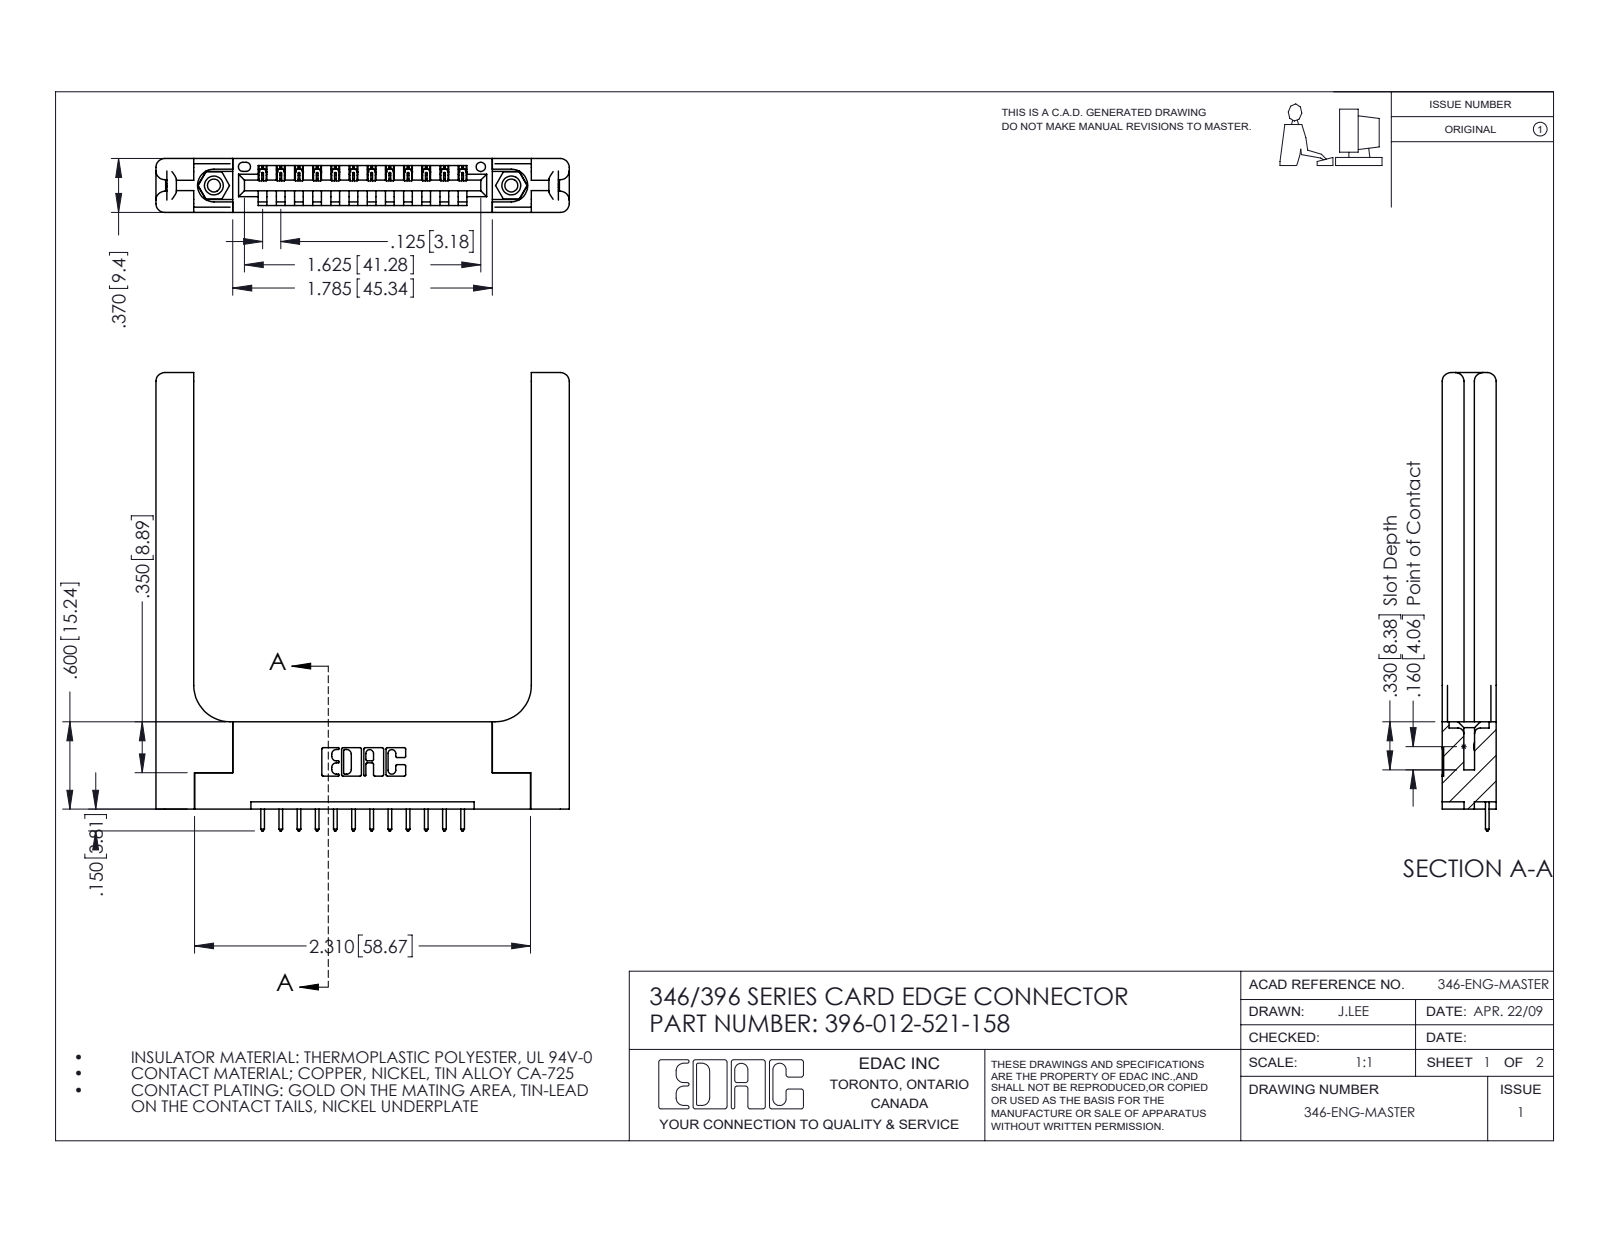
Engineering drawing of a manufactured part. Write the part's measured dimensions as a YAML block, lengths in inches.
part_name: "346-220-058_345-220-058; 345-250-001_345-250-001-102; 345-292-001_345-293-121; 346 Part_Flush Mounting Lugs - 0.156 Dia-TH (+1 more)"
step_written_by: "SolidWorks 2016 (CONFIG_CONTROL_DESIGN)"
units: inches
bodies: {solids: 17, faces: 1074, planar: 704, cylindrical: 310, other: 60}
overall_size: [3.15, 2.841, 0.37]
volume: 0.866
surface_area: 20.22
round_holes:
  - {diameter: 0.089, count: 2}
  - {diameter: 0.125, count: 2}
  - {diameter: 0.156, count: 2}
  - {diameter: 0.064, count: 1}
round_bosses_or_shafts:
  - {diameter: 0.155, count: 2}
partial_cylinders:
  - {radius: 0.006, count: 24}
  - {radius: 0.01, count: 24}
  - {radius: 0.01, count: 22}
  - {radius: 0.06, count: 16}
  - {radius: 0.007, count: 6}
  - {radius: 0.031, count: 6}
  - {radius: 0.026, count: 3}
  - {radius: 0.03, count: 2}
face_to_face_distances: [0.37, 0.15, 0.072, 0.148, 0.22, 0.048, 0.322, 0.25, 0.102, 0.173]
hole_center_spacings: [0.246, 1.839, 2.045]
